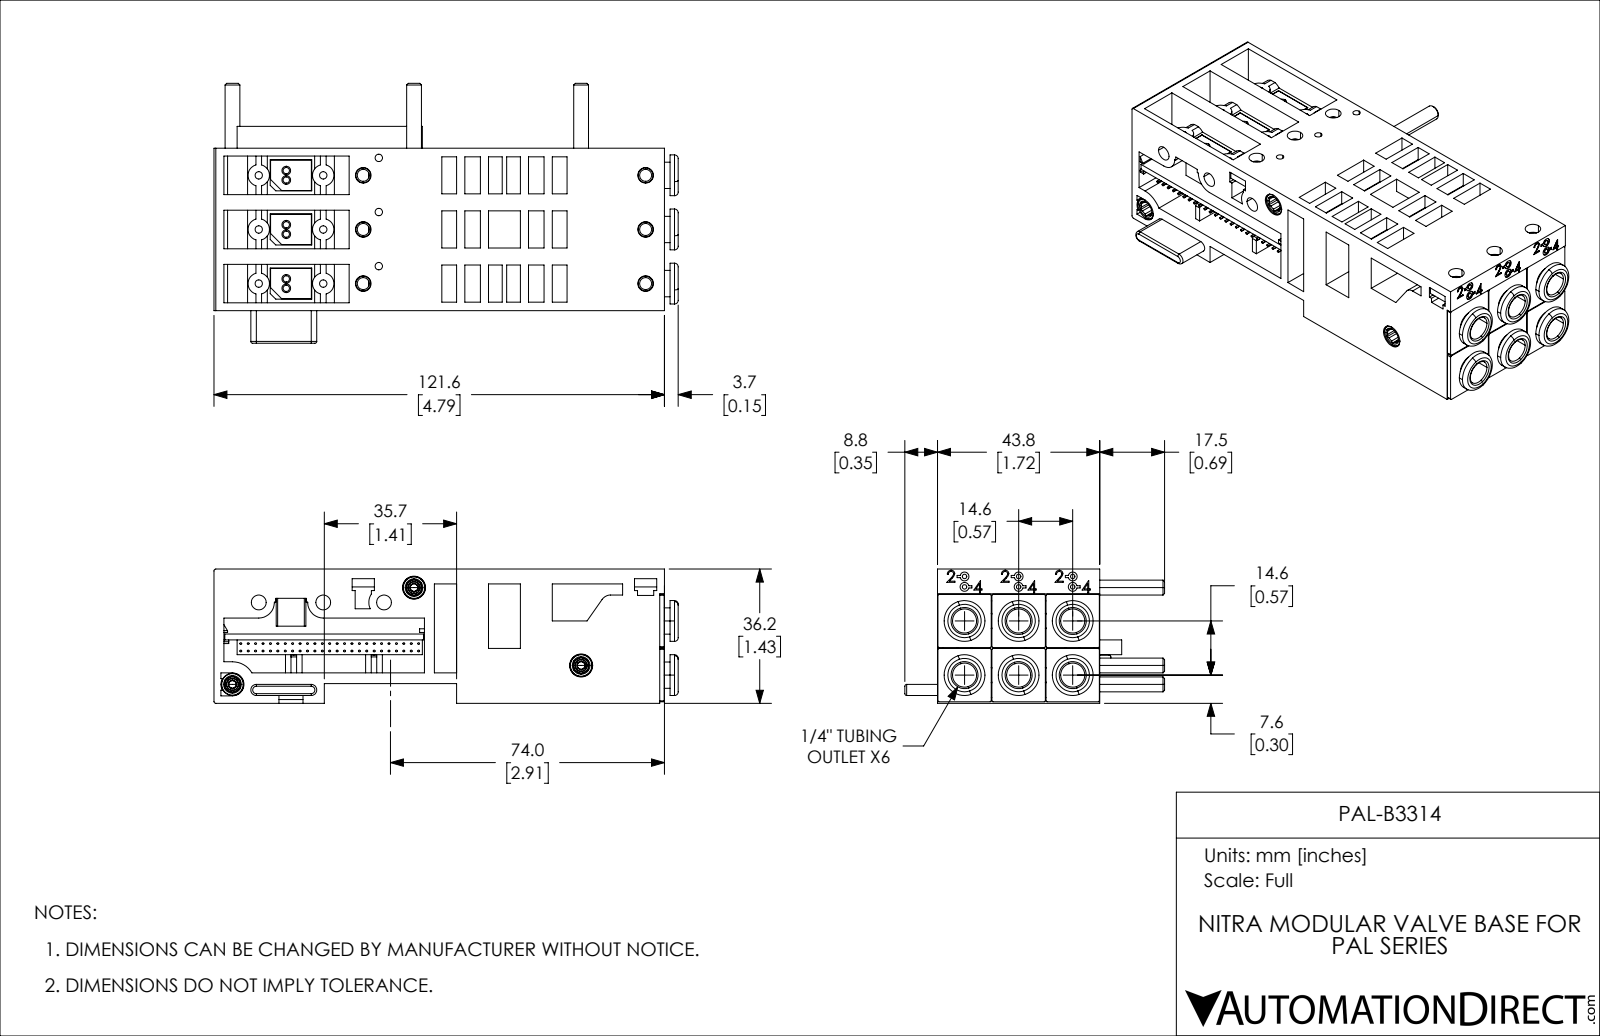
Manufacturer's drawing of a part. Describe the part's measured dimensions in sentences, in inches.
The part is named "PAL-B3314". Its 3-D file was written by "SolidWorks 2019 (CONFIG_CONTROL_DESIGN)". It is 7 solids with 1480 faces: 802 planar, 520 cylindrical and 158 other. Overall it measures 4.933 by 2.76 by 1.425 inches. Its volume is 7.178 cubic inches and its surface area 100.1 square inches. Round holes: 50 of diameter 0.02, 9 of diameter 0.079, 9 of diameter 0.128, 6 of diameter 0.094, 6 of diameter 0.165, 6 of diameter 0.256, 3 of diameter 0.157, 2 of diameter 0.244, 1 of diameter 0.189. Round bosses or shafts: 6 of diameter 0.433, 6 of diameter 0.28, 6 of diameter 0.228, 6 of diameter 0.047, 3 of diameter 0.236, 3 of diameter 0.157, 2 of diameter 0.177. Partial cylindrical surfaces (rounded edges, fillets, slot ends): 11 of radius 0.02, 6 of radius 0.098, 6 of radius 0.295, 6 of radius 0.394, 5 of radius 0.039, 5 of radius 0.157, 4 of radius 0.037, 3 of radius 0.026. The main face-to-face distances are 1.425, 0.063, 0.752, 0.323, 1.724, 0.673, 0.736, 0.575, 0.413, 0.339. The hole center spacings are 0.079, 0.157, 0.575, 0.236, 0.315, 0.472, 0.394, 0.551.
